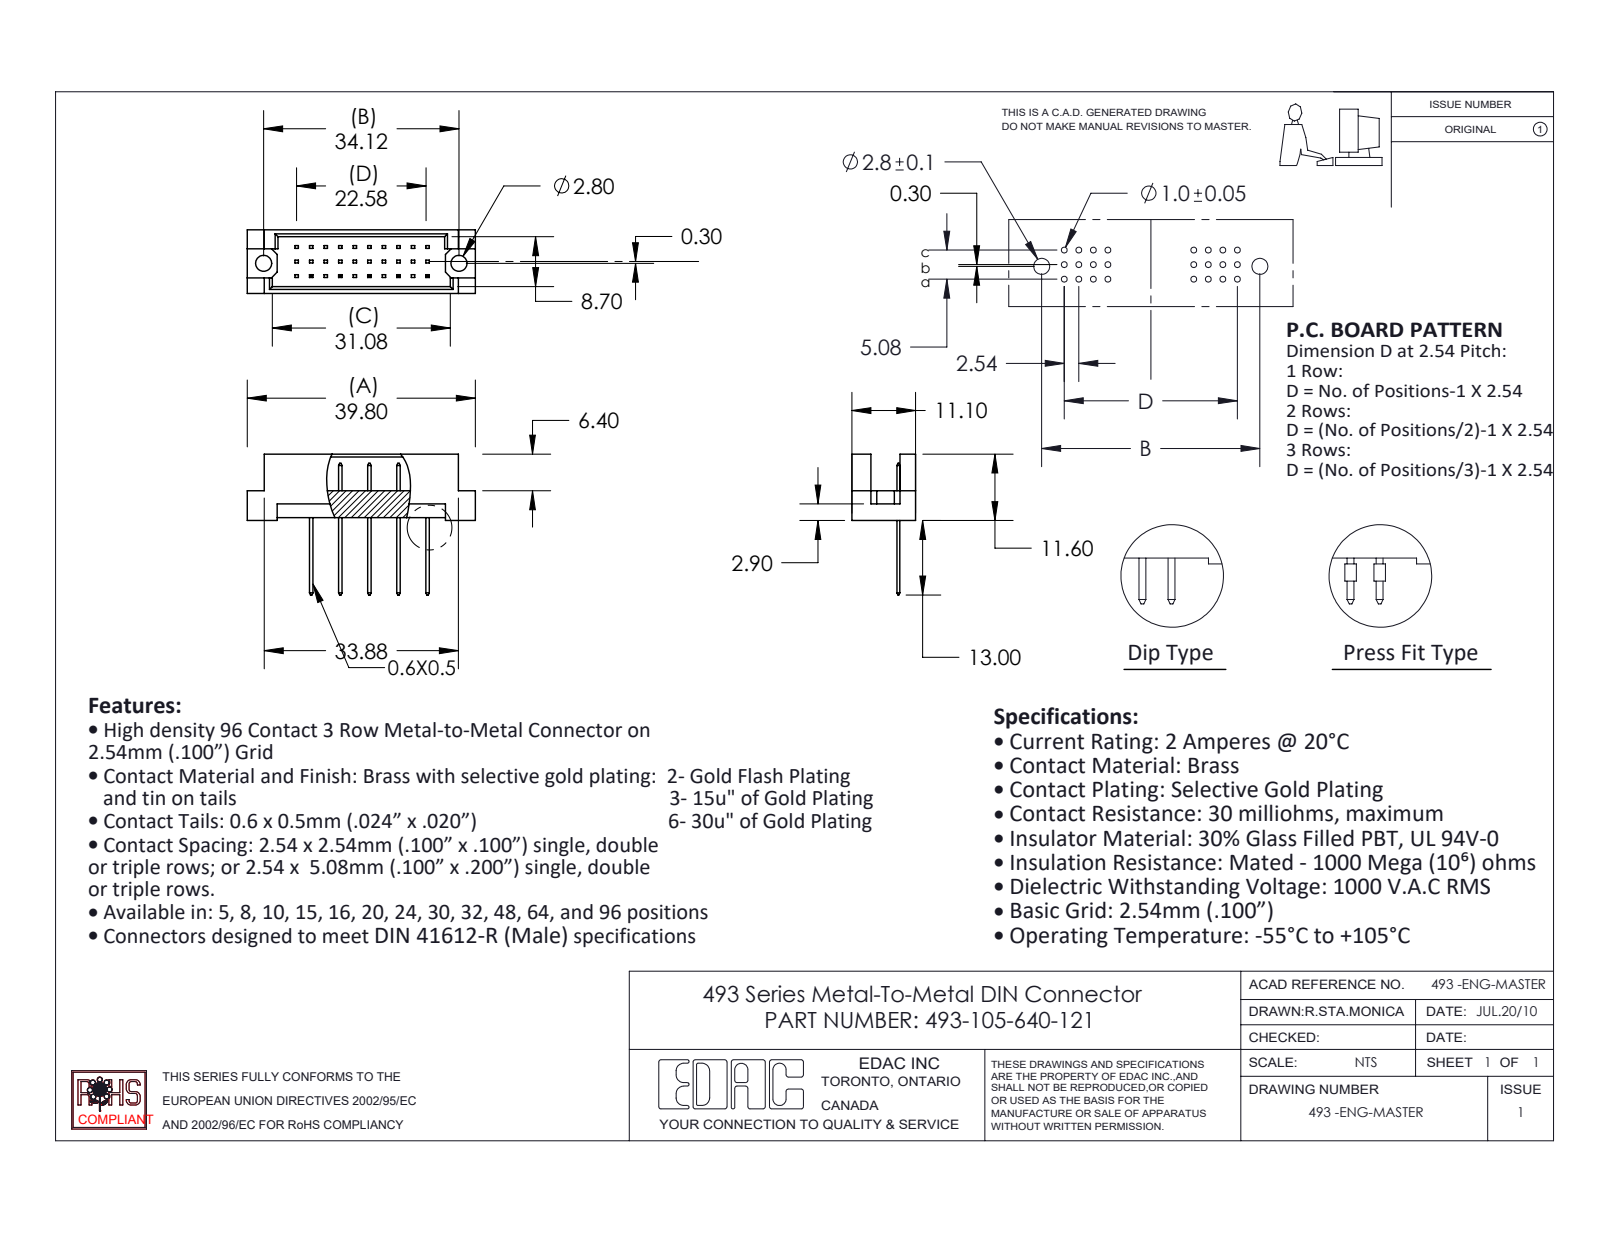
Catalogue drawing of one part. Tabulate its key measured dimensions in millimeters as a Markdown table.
| quantity | value |
| --- | --- |
| part name | 493-290_40; 493 Part_30; 493-105-640-121 |
| STEP written by | SolidWorks 2020 (CONFIG_CONTROL_DESIGN) |
| units | millimeters |
| bodies | 6 solids, 242 faces (238 planar, 4 cylindrical, 0 other) |
| overall size | 39.8 × 24.6 × 11.1 |
| volume | 2 407 mm³ |
| surface area | 2 989 mm² |
| round holes (diameter × count) | 2.8 × 2 |
| main face-to-face distances | 1.2, 9.9, 11.1, 8.7, 0.5, 4.7, 5.08, 2.4, 2.76, 3.26 |
| hole center spacings | 34.12 |
